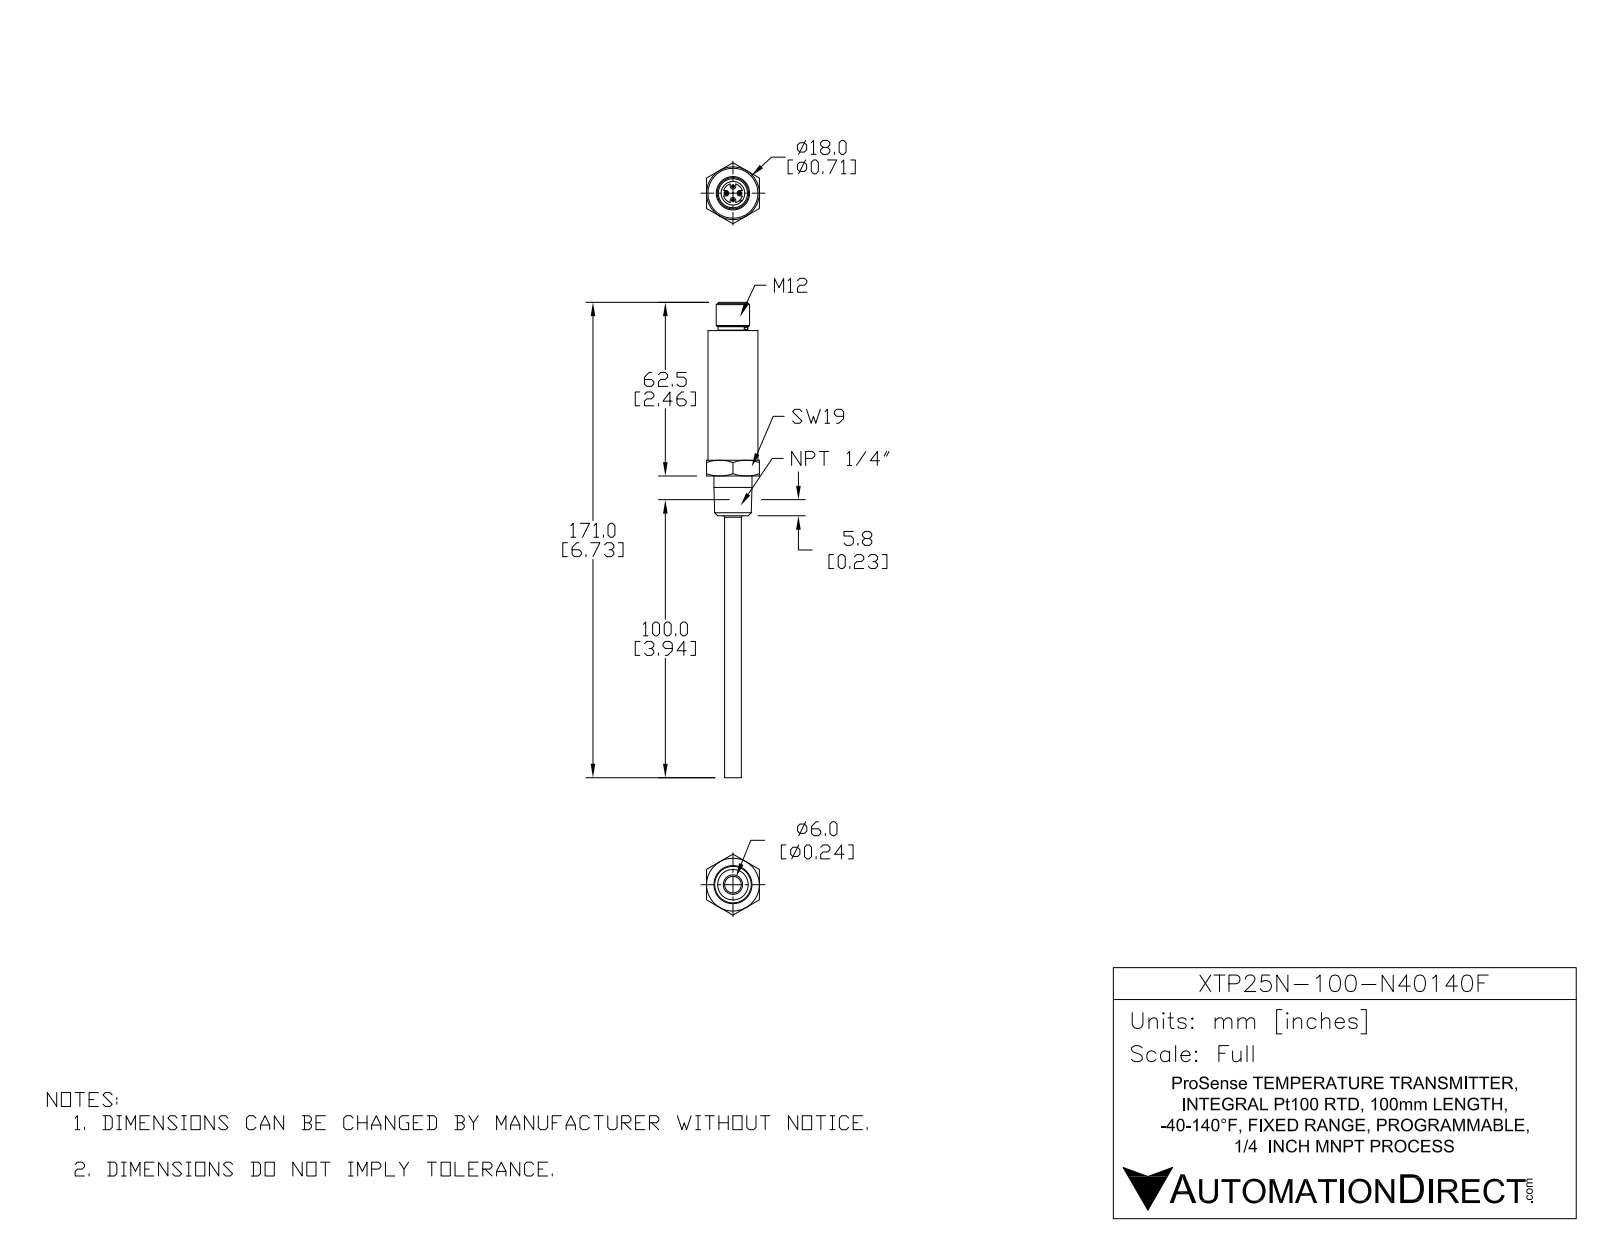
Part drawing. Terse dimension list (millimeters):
name: XTP25N-100-N40140F
written by: SolidWorks 2015 (AUTOMOTIVE_DESIGN)
unit: mm
bodies: 1 solid, 117 faces (43 planar, 34 cylindrical, 40 other)
size: 171 × 21.94 × 19
volume: 18 646 mm³; area: 6 946 mm²
holes: 1× ⌀4, 1× ⌀8.5
bosses: 4× ⌀1.02, 1× ⌀18, 1× ⌀13.72, 1× ⌀12, 1× ⌀10.7, 1× ⌀10.5, 1× ⌀6
rounds: 4× R1, 1× R3.5, 1× R4.25
face distances: 19, 52.3, 14.3, 66.6, 20, 5.7, 46.6, 76.8, 62.5, 56.8
